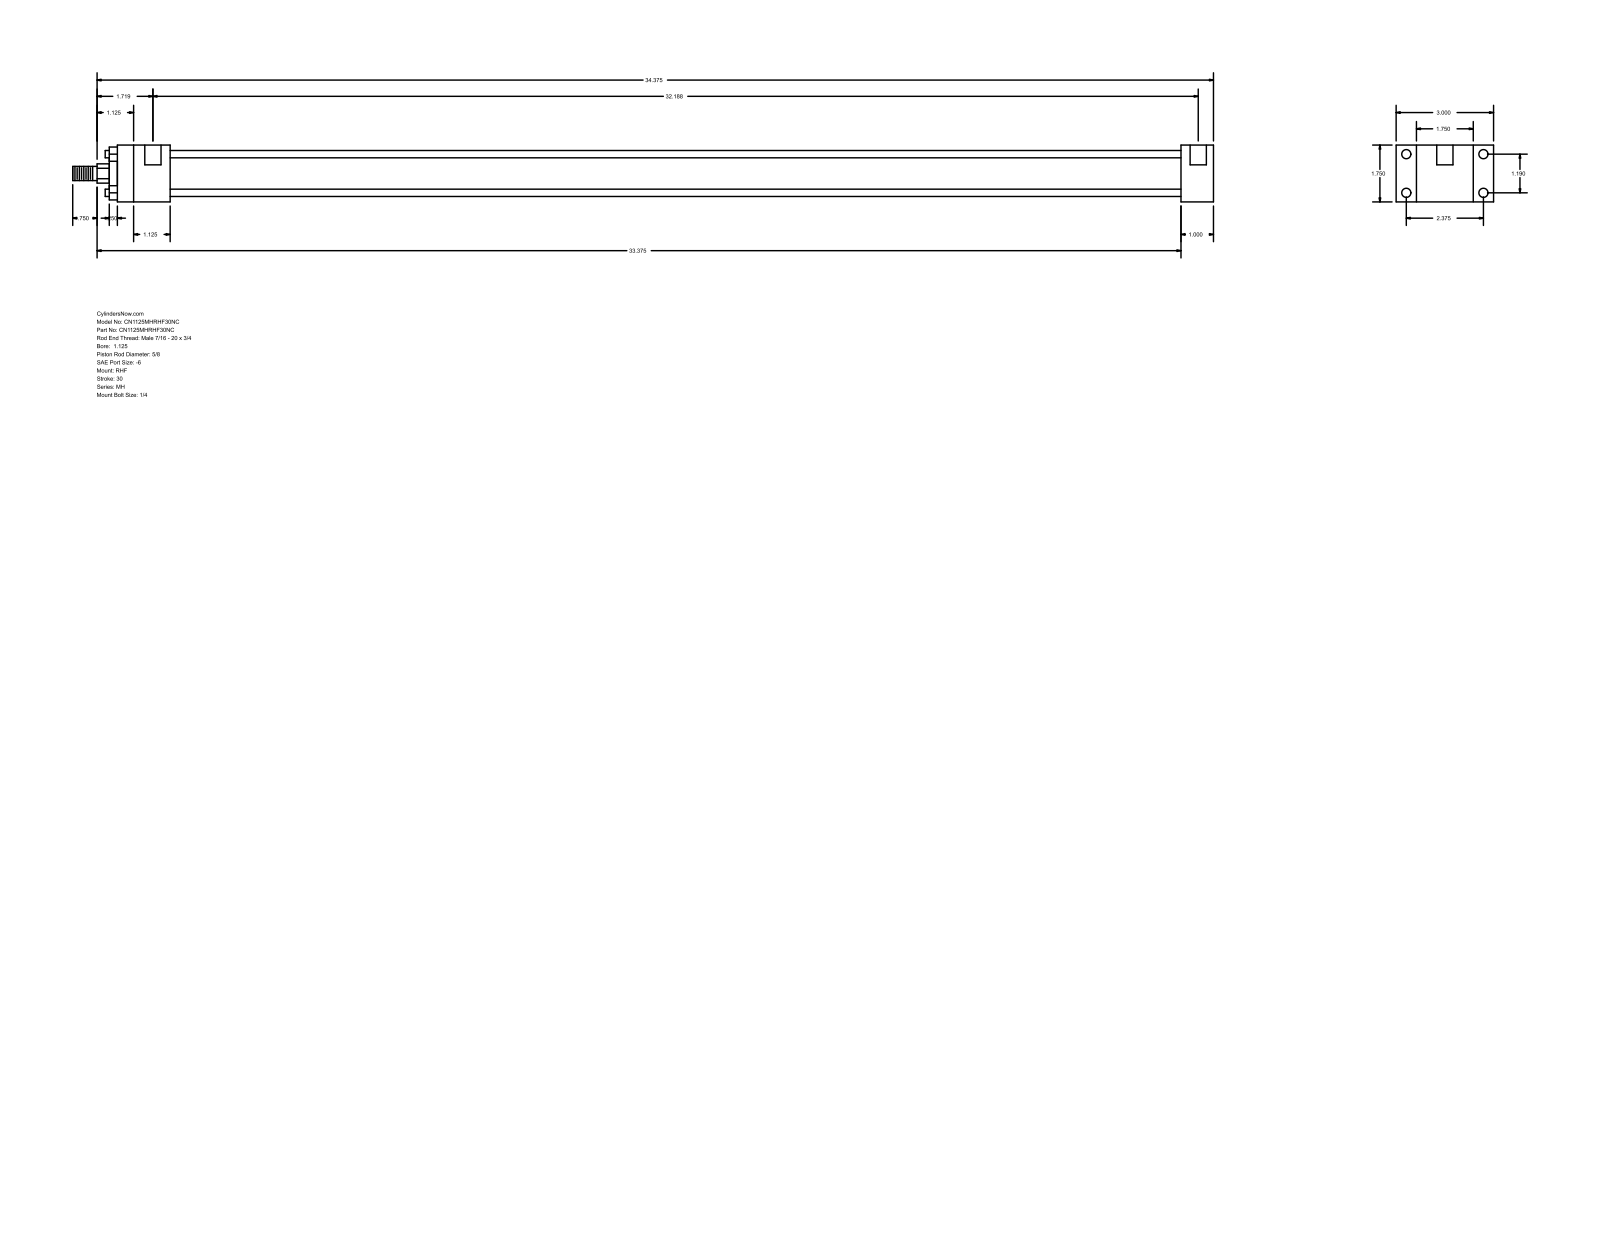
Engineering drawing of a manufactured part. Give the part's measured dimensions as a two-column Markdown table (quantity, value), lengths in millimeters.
| quantity | value |
| --- | --- |
| part name | MH_RHF__0112_0.625 |
| STEP written by | GSSL Pune (CONFIG_CONTROL_DESIGN) |
| units | millimeters |
| bodies | 0 solids, 88 faces (60 planar, 28 cylindrical, 0 other) |
| overall size | 892.17 × 76.2 × 44.45 |
| round holes (diameter × count) | 5.56 × 4, 7.14 × 4, 12.7 × 2 |
| round bosses / shafts (diameter × count) | 5.71 × 4, 34.92 × 1, 28.57 × 1, 15.88 × 1, 11.11 × 1 |
| partial cylindrical surfaces (radius × count) | 7.54 × 1 |
| main face-to-face distances | 44.46, 15.87, 60.33, 25.39, 76.2, 790.58, 815.97, 41.27, 831.85, 857.24 |
| hole center spacings | 30.22, 60.32, 67.47, 814.39, 3.17, 817.56 |
